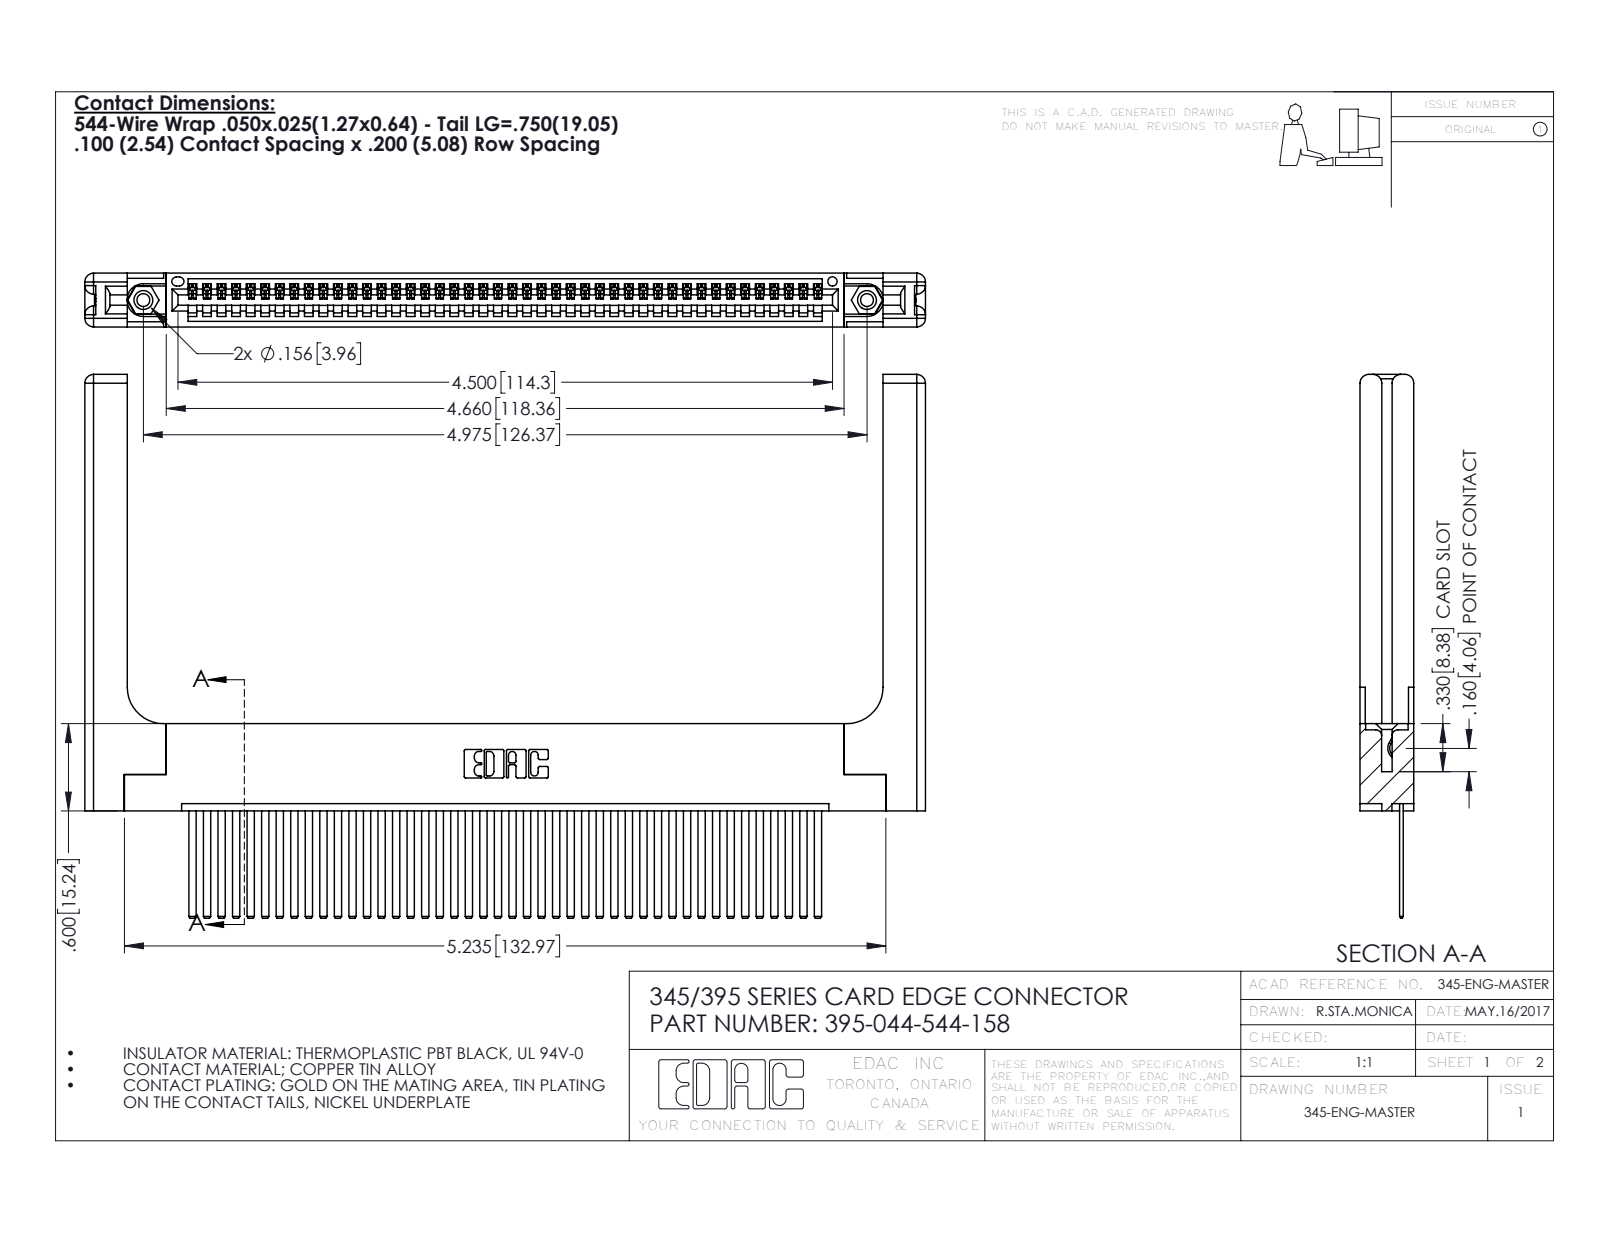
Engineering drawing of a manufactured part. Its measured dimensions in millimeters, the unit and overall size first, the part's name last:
Units: millimetres
Overall size (bounding box): 146.8 × 94.9 × 9.4
Round holes (diameter × count): ⌀2.3 ×2, ⌀3.2 ×2, ⌀4 ×2, ⌀1.6 ×1
Round bosses / shafts (diameter × count): ⌀3.9 ×2
Partial cylindrical surfaces — rounded edges, fillets, slot ends (radius × count): R0.2 ×88, R0.3 ×22, R1.5 ×16, R0.2 ×6, R0.8 ×6, R0.7 ×3, R0.8 ×2, R0.8 ×2
Main face-to-face distances: 1.8, 7.6, 9.4, 2.5, 6.9, 0.6, 5.1, 5.7, 3.8, 3.8
Hole centre spacings: 6.9, 120.4, 126.4
Volume: 22 970 mm³ · Surface area: 26 090 mm²
Bodies: 49 solids, 2670 faces (1812 planar, 798 cylindrical, 60 other)
Part name (STEP PRODUCT): 345-220-058_345-220-058; 345-292-001_345-293-144; 345-250-001_345-250-001-102; 345 Part_Flush Mounting Lugs - 0.156 Dia-TH (+1 more)
STEP written by: SolidWorks 2016 (CONFIG_CONTROL_DESIGN)
